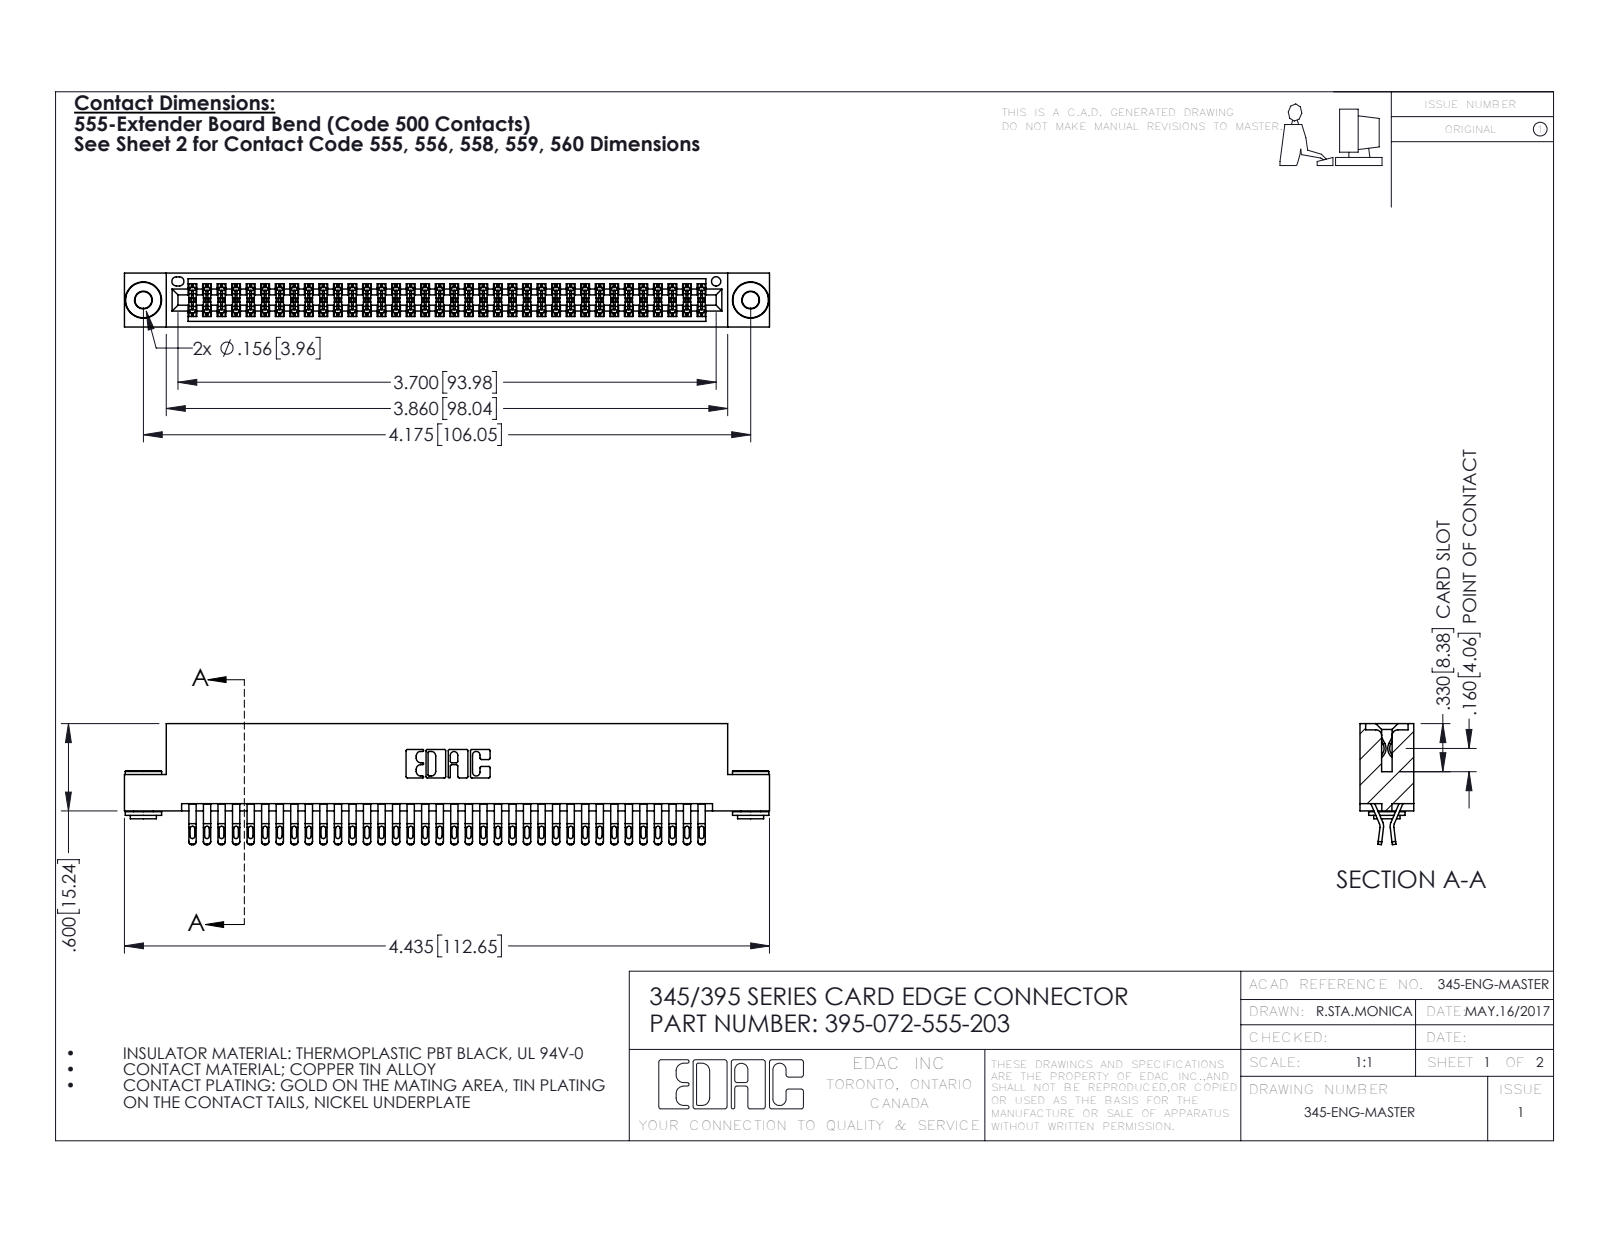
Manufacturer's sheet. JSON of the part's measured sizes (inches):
{"part_name": "345-292-001_555 Tail; 395-072-555-203; 345 Part_Flush Mounting Lugs - 0.156 Dia-TH; 345-250-002_345-250-002-102", "step_written_by": "SolidWorks 2016 (CONFIG_CONTROL_DESIGN)", "units": "inches", "bodies": {"solids": 75, "faces": 4196, "planar": 2322, "cylindrical": 1866, "other": 8}, "overall_size": [4.435, 0.832, 0.37], "volume_in3": 0.678, "surface_area_in2": 26.73, "round_holes": [[0.116, 2], [0.156, 2], [0.064, 1]], "round_bosses_or_shafts": [[0.25, 2], [0.18, 2], [0.136, 2]], "partial_cylinders_radius": [[0.016, 180], [0.02, 144], [0.006, 108], [0.01, 22], [0.007, 6], [0.031, 6], [0.026, 3], [0.01, 2]], "face_to_face_distances": [0.072, 0.298, 0.2, 0.025, 0.37, 0.098, 0.272, 0.225, 0.175, 0.149], "hole_center_spacings": [0.27, 3.939, 4.175]}
